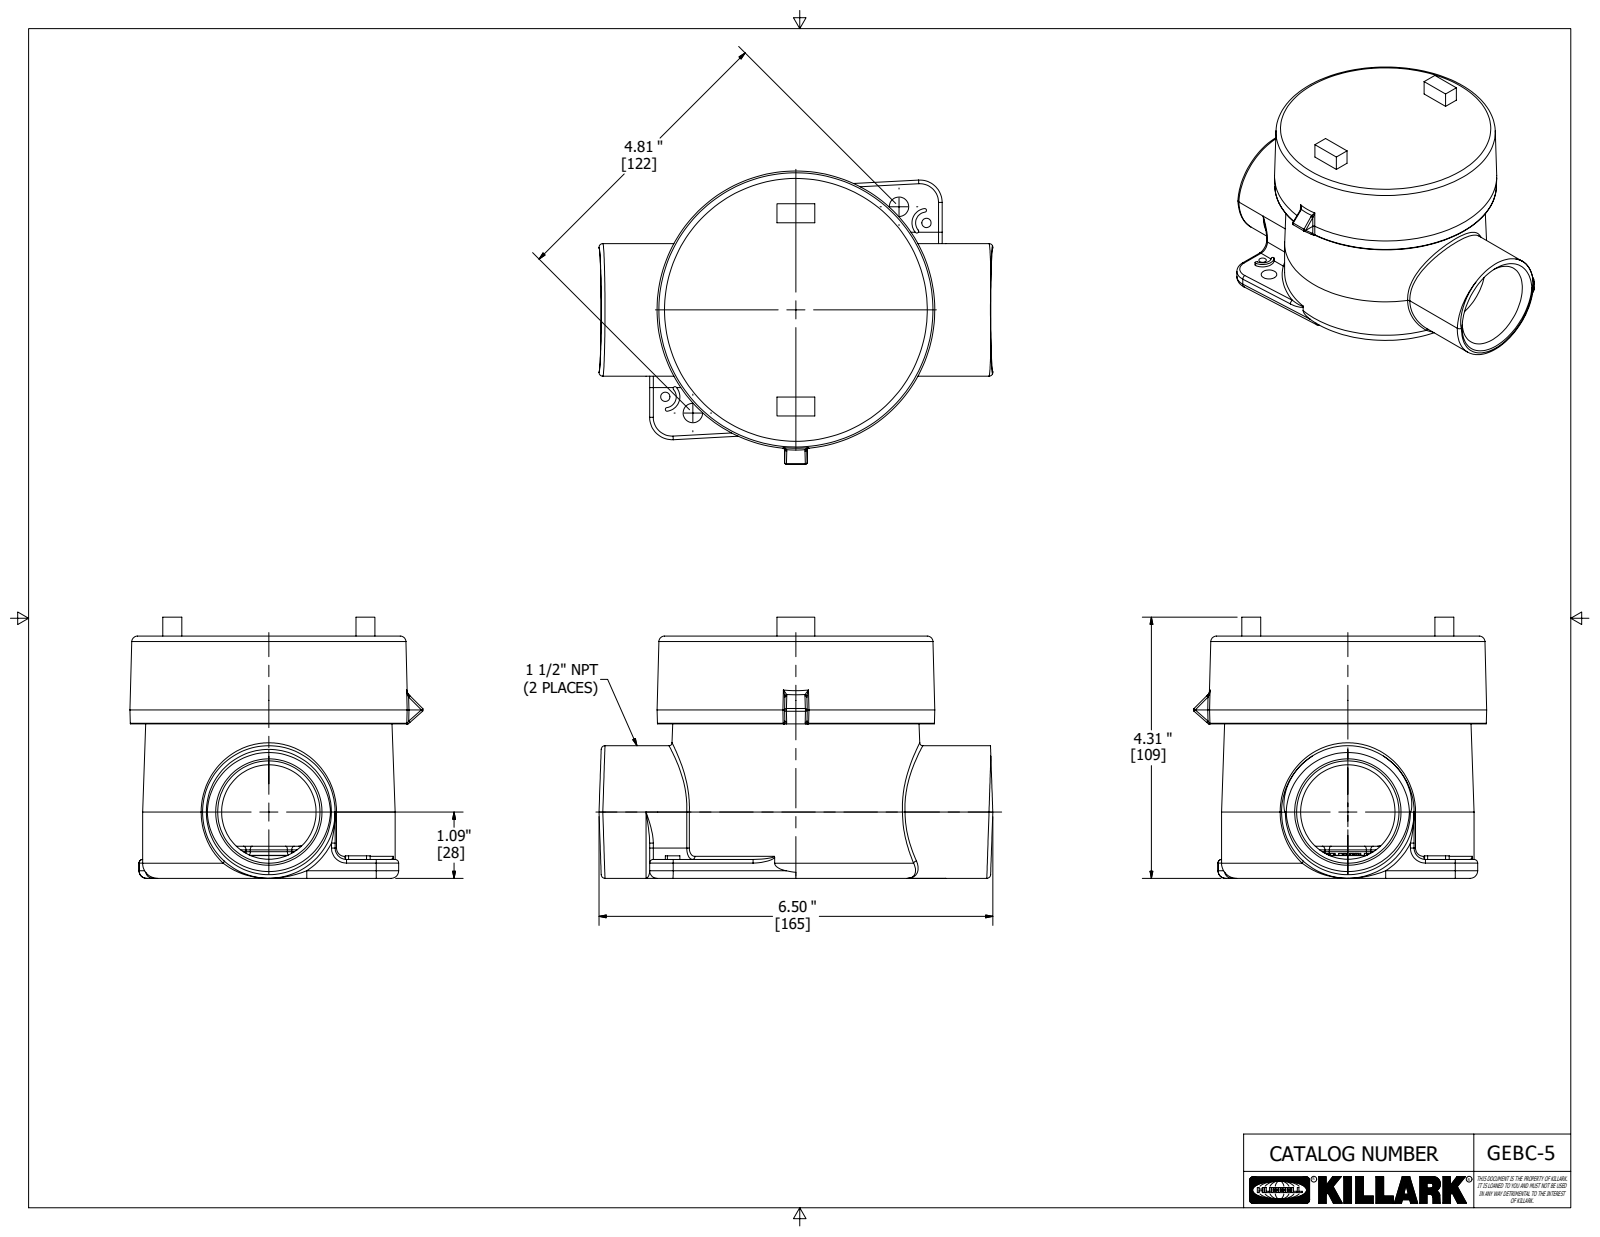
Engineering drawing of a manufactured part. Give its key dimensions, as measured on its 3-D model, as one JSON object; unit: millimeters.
{"part_name": "GEBC-5; 21162; 21147-override", "step_written_by": "Autodesk Inventor 2020 (AUTOMOTIVE_DESIGN)", "units": "millimeters", "bodies": {"solids": 2, "faces": 833, "planar": 398, "cylindrical": 89, "other": 346}, "overall_size": [165.1, 122.9, 109.5], "volume_mm3": 547800, "surface_area_mm2": 129900, "round_holes": [[3.9, 2], [8.2, 2], [39.6, 1], [97.1, 1], [102.7, 1]], "round_bosses_or_shafts": [[55.6, 1]], "partial_cylinders_radius": [[1.5, 33], [0.8, 14], [3.2, 4], [0.8, 3], [1.3, 2], [4.6, 2], [4.7, 2], [6.1, 2]], "face_to_face_distances": [101.5, 90.4, 11.1, 64.7, 25.7, 36.8, 88.9, 9.7, 55.1, 80.8], "hole_center_spacings": [13.4, 126.2, 61.1, 61.1, 65.8, 65.8, 122.2, 131.5]}
